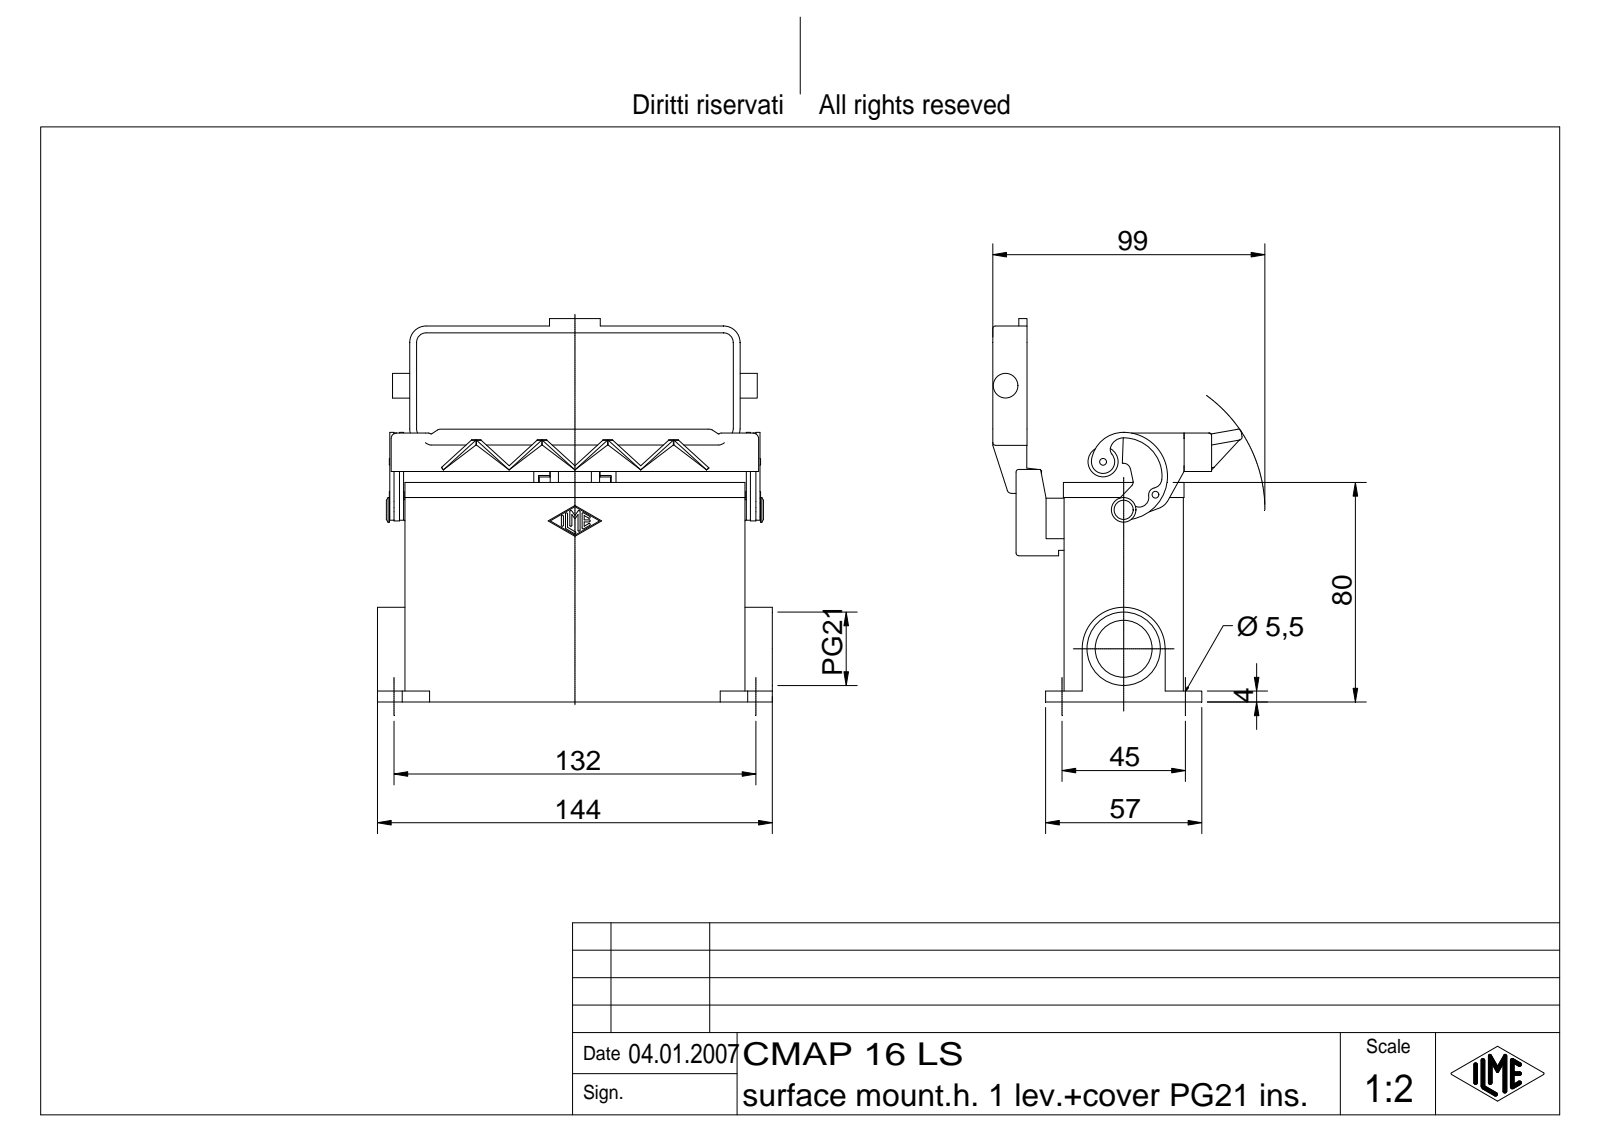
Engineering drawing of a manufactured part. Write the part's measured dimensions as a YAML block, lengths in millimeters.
part_name: "CMAP 16 LS"
step_written_by: "Autodesk Inventor 7 (AUTOMOTIVE_DESIGN)"
units: millimeters
bodies: {solids: 6, faces: 623, planar: 279, cylindrical: 180, other: 164}
overall_size: [144, 139.7, 90.95]
volume: 193257
surface_area: 106964
round_holes:
  - {diameter: 5.5, count: 4}
  - {diameter: 2, count: 1}
  - {diameter: 4, count: 1}
  - {diameter: 20.78, count: 1}
  - {diameter: 26.78, count: 1}
round_bosses_or_shafts:
  - {diameter: 9, count: 2}
  - {diameter: 5, count: 2}
  - {diameter: 11, count: 1}
  - {diameter: 7, count: 1}
  - {diameter: 4, count: 1}
  - {diameter: 3, count: 1}
  - {diameter: 2.5, count: 1}
partial_cylinders:
  - {radius: 1, count: 18}
  - {radius: 0.38, count: 14}
  - {radius: 2, count: 12}
  - {radius: 6, count: 12}
  - {radius: 1.5, count: 6}
  - {radius: 3.5, count: 6}
  - {radius: 3, count: 4}
  - {radius: 0.5, count: 3}
face_to_face_distances: [3, 40.5, 43.5, 4, 37.5, 26, 66.5, 69.5, 29, 3.5]
hole_center_spacings: [45, 132, 139.46, 57.3]
